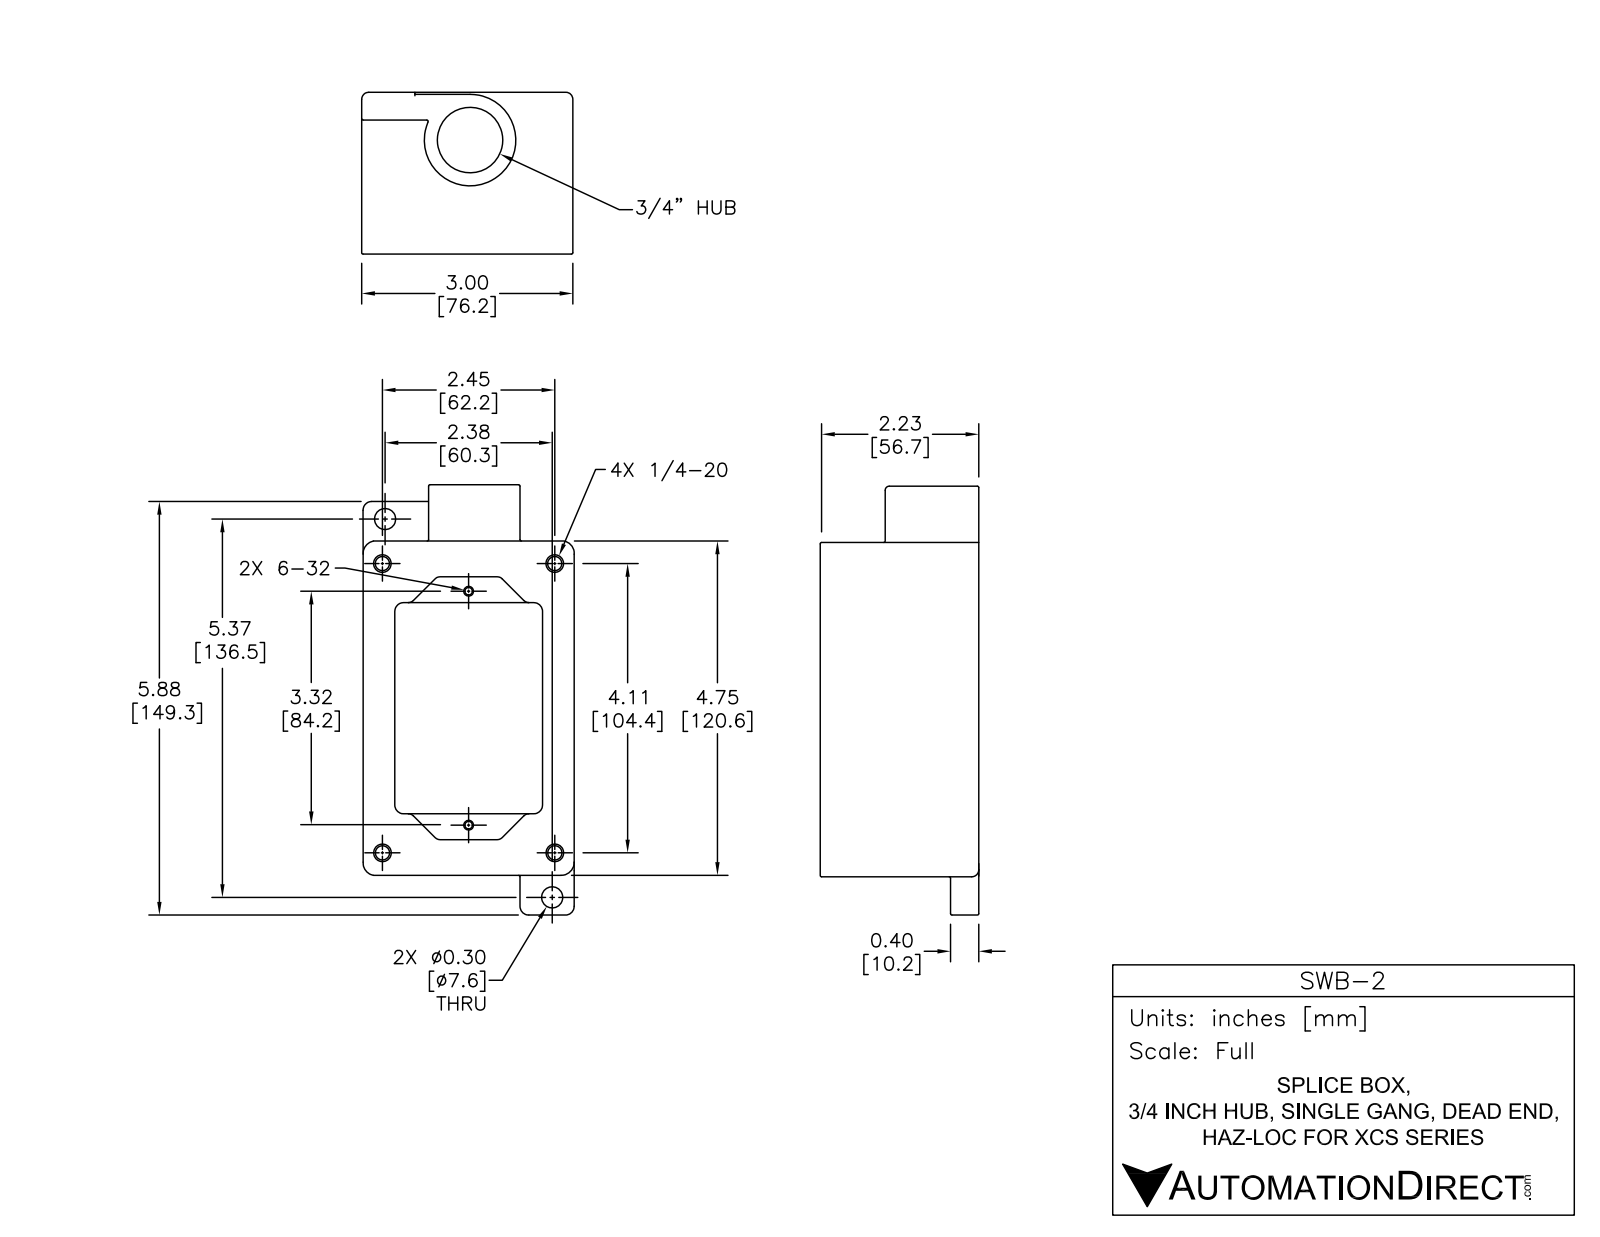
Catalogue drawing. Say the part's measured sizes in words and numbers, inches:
The part is named "SWB-2". Its 3-D file was written by "SolidWorks 2015 (AUTOMOTIVE_DESIGN)". It is 1 solid with 266 faces: 112 planar, 79 cylindrical and 75 other. Overall it measures 6.175 by 3.08 by 2.3 inches. Its volume is 13.69 cubic inches and its surface area 111.6 square inches. Round holes: 4 of diameter 0.201, 2 of diameter 0.107, 2 of diameter 0.3, 1 of diameter 0.93. Round bosses or shafts: 1 of diameter 1.3, 1 of diameter 0.4. Partial cylindrical surfaces (rounded edges, fillets, slot ends): 25 of radius 0.02, 12 of radius 0.1, 5 of radius 0.188, 4 of radius 0.125, 3 of radius 0.187, 1 of radius 0.023, 1 of radius 0.17, 1 of radius 0.25. The main face-to-face distances are 0.25, 2.83, 3.08, 4.5, 2.3, 2.05, 2.58, 4.75, 0.3, 1.75. The hole center spacings are 3.914, 1.287, 4.11, 0.697, 0.78, 1.286, 1.287, 1.598.
